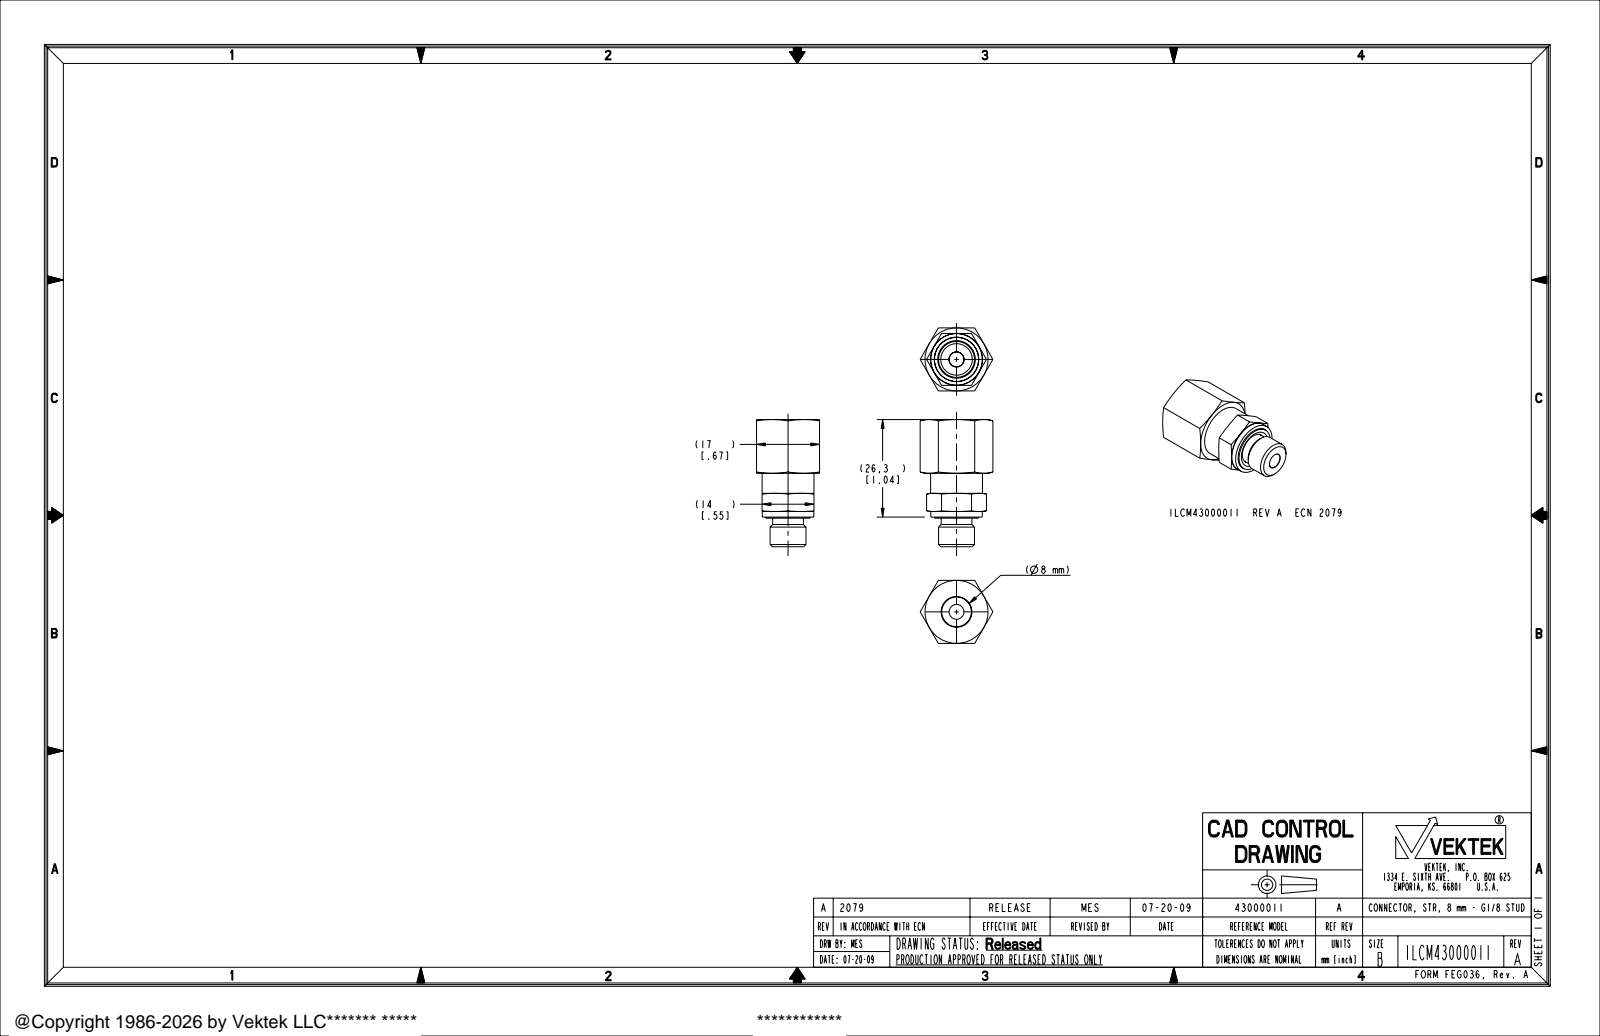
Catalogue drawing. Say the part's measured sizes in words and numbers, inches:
The part is named "ILCM43000011". Its 3-D file was written by "PRO/ENGINEER BY PARAMETRIC TECHNOLOGY CORPORATION, 2007460 (AUTOMOTIVE_DESIGN_CC2)". It is 1 solid with 101 faces: 25 planar, 28 cylindrical and 48 other. Overall it measures 1.35 by 0.773 by 0.669 inches. Its volume is 0.291 cubic inches and its surface area 5.299 square inches. Round holes: 1 of diameter 0.157, 1 of diameter 0.315, 1 of diameter 0.331, 1 of diameter 0.472, 1 of diameter 0.487. Round bosses or shafts: 1 of diameter 0.551, 1 of diameter 0.547, 1 of diameter 0.469, 1 of diameter 0.433, 1 of diameter 0.398, 1 of diameter 0.382, 1 of diameter 0.327. The main face-to-face distances are 0.669, 0.059, 0.61, 0.551, 0.571, 0.465, 0.78, 1.35, 0.315, 1.035.
